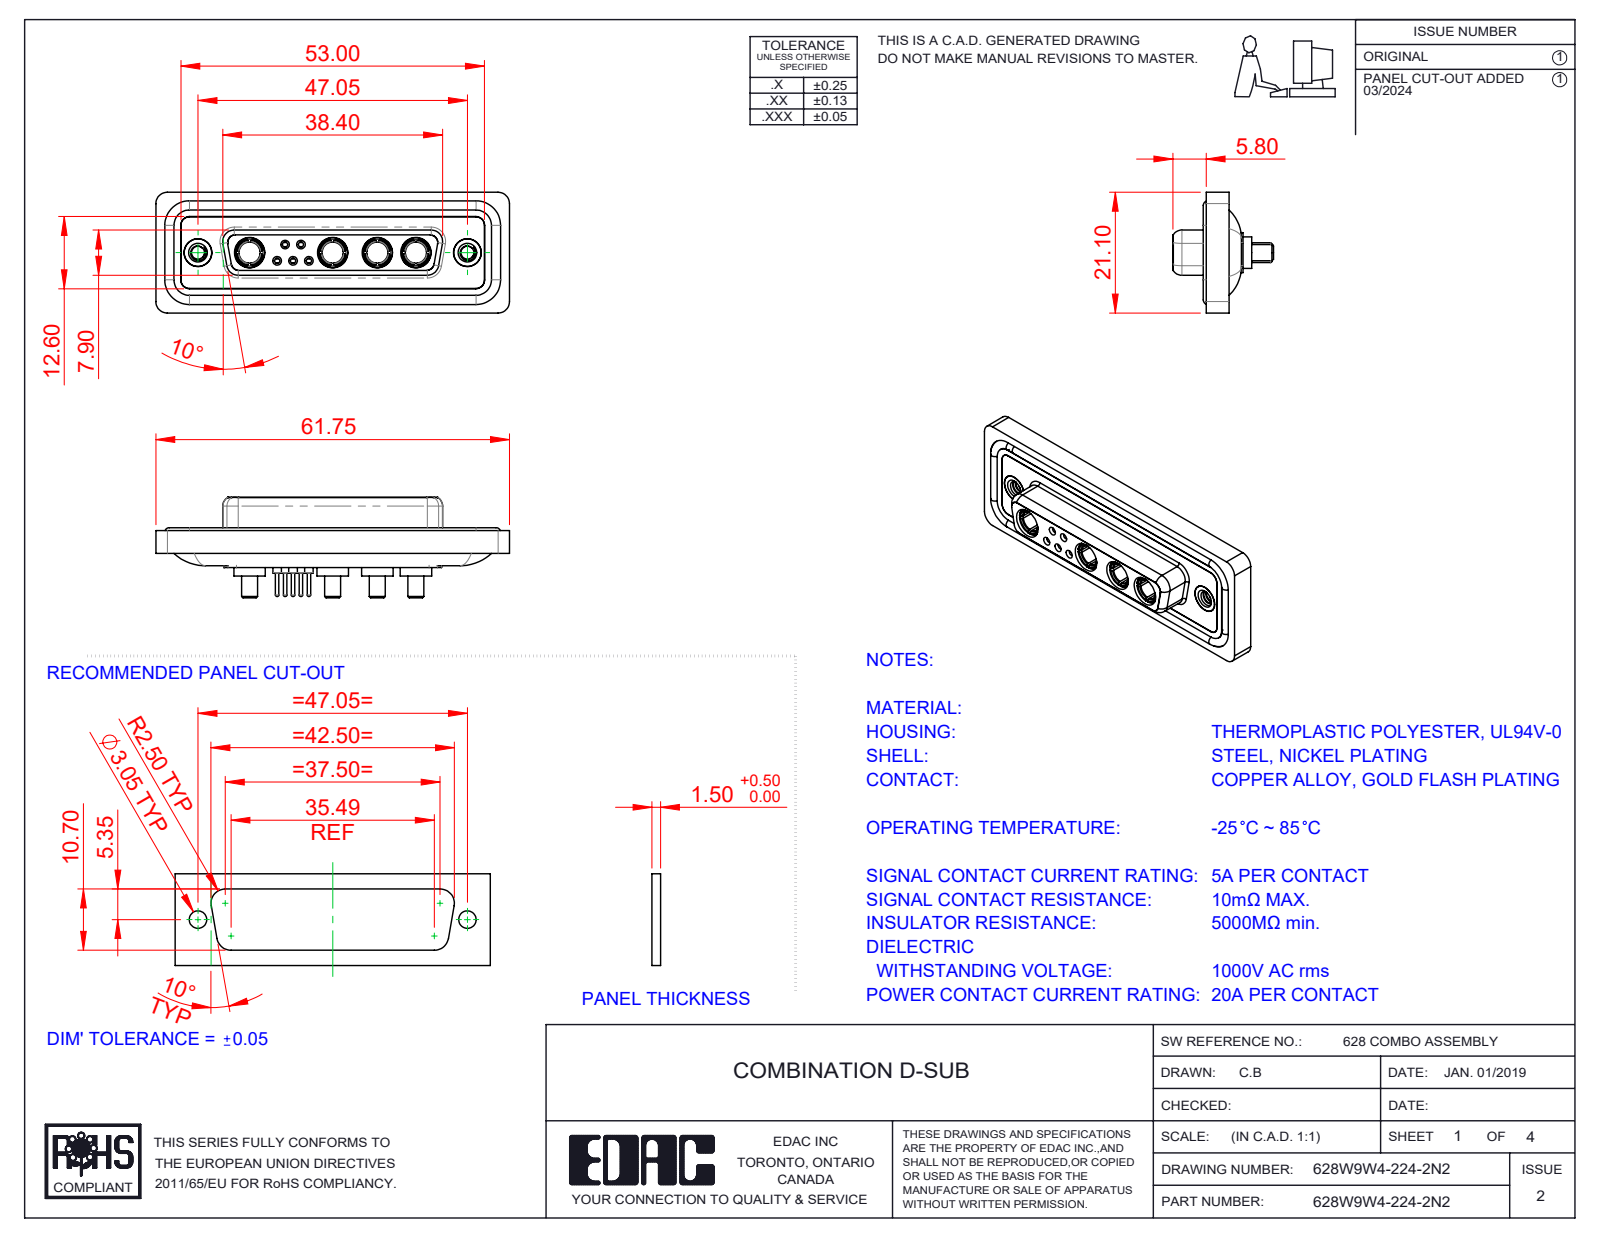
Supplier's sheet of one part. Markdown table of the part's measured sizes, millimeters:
| quantity | value |
| --- | --- |
| part name | 628Combo Shell Rear_25 Contacts; 628Combo Housing_9W4; Power Socket_20A S; 628W9W4-224-2N2 (+5 more) |
| STEP written by | SolidWorks 2023 (CONFIG_CONTROL_DESIGN) |
| units | millimeters |
| bodies | 20 solids, 957 faces (296 planar, 375 cylindrical, 286 other) |
| overall size | 61.75 × 21.1 × 17.55 |
| volume | 8 223 mm³ |
| surface area | 13 562 mm² |
| round holes (diameter × count) | 4.85 × 6, 0.9 × 5, 1.1 × 5, 1.5 × 5, 2 × 5, 3.7 × 4, 5.3 × 4, 1.6 × 3, 1.7 × 2, 2.26 × 2, 4 × 2, 4.05 × 2 |
| round bosses / shafts (diameter × count) | 1.6 × 6, 2.2 × 5, 0.6 × 5, 5.5 × 4, 5.2 × 4, 4.96 × 4, 4.75 × 4, 3.75 × 4 |
| partial cylindrical surfaces (radius × count) | 1.5 × 22, 2 × 18, 1.35 × 8, 1.6 × 8, 0.25 × 4, 0.5 × 4, 0.6 × 4, 0.65 × 4 |
| main face-to-face distances | 0.4, 1.8, 7.45, 5.65, 0.5, 7.05, 6.6, 1.6, 1.1, 2.9 |
| hole center spacings | 3.16, 2.77, 5.03, 2.76, 4.4, 5.02, 5.54, 5.73 |
